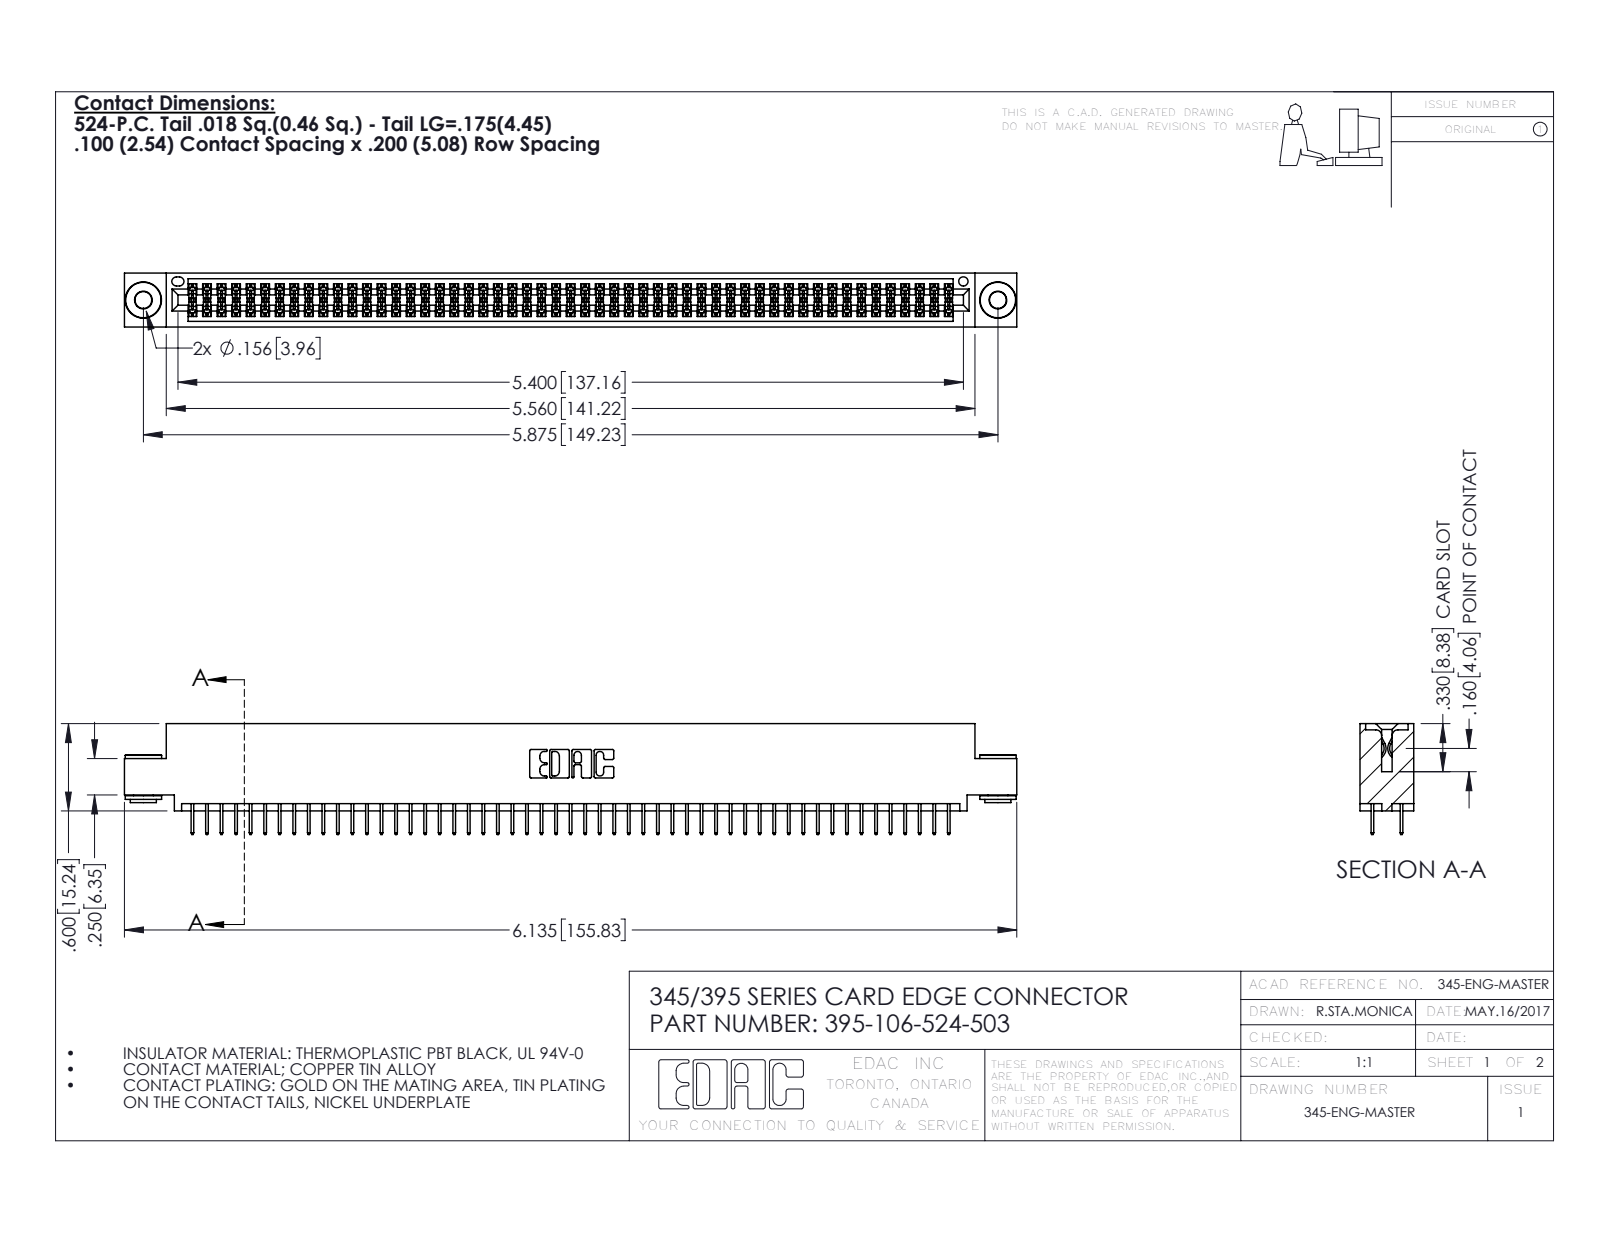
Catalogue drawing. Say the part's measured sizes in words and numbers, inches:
The part is named "345-292-001_345-293-124; 345-250-002_345-250-002-102; 345 Part_0.110 Offset - 0.156 Dia-TH; 395-106-524-503". Its 3-D file was written by "SolidWorks 2016 (CONFIG_CONTROL_DESIGN)". It is 109 solids with 5892 faces: 4228 planar, 1656 cylindrical and 8 other. Overall it measures 6.135 by 0.762 by 0.37 inches. Its volume is 0.917 cubic inches and its surface area 34.56 square inches. Round holes: 2 of diameter 0.116, 2 of diameter 0.156, 1 of diameter 0.064. Round bosses or shafts: 2 of diameter 0.25, 2 of diameter 0.18, 2 of diameter 0.136. Partial cylindrical surfaces (rounded edges, fillets, slot ends): 159 of radius 0.006, 22 of radius 0.01, 6 of radius 0.007, 6 of radius 0.031, 3 of radius 0.026, 2 of radius 0.014, 2 of radius 0.019, 2 of radius 0.022. The main face-to-face distances are 0.072, 0.298, 0.2, 0.37, 0.025, 0.098, 0.272, 0.225, 0.072, 0.175. The hole center spacings are 0.27, 5.639, 5.875.
